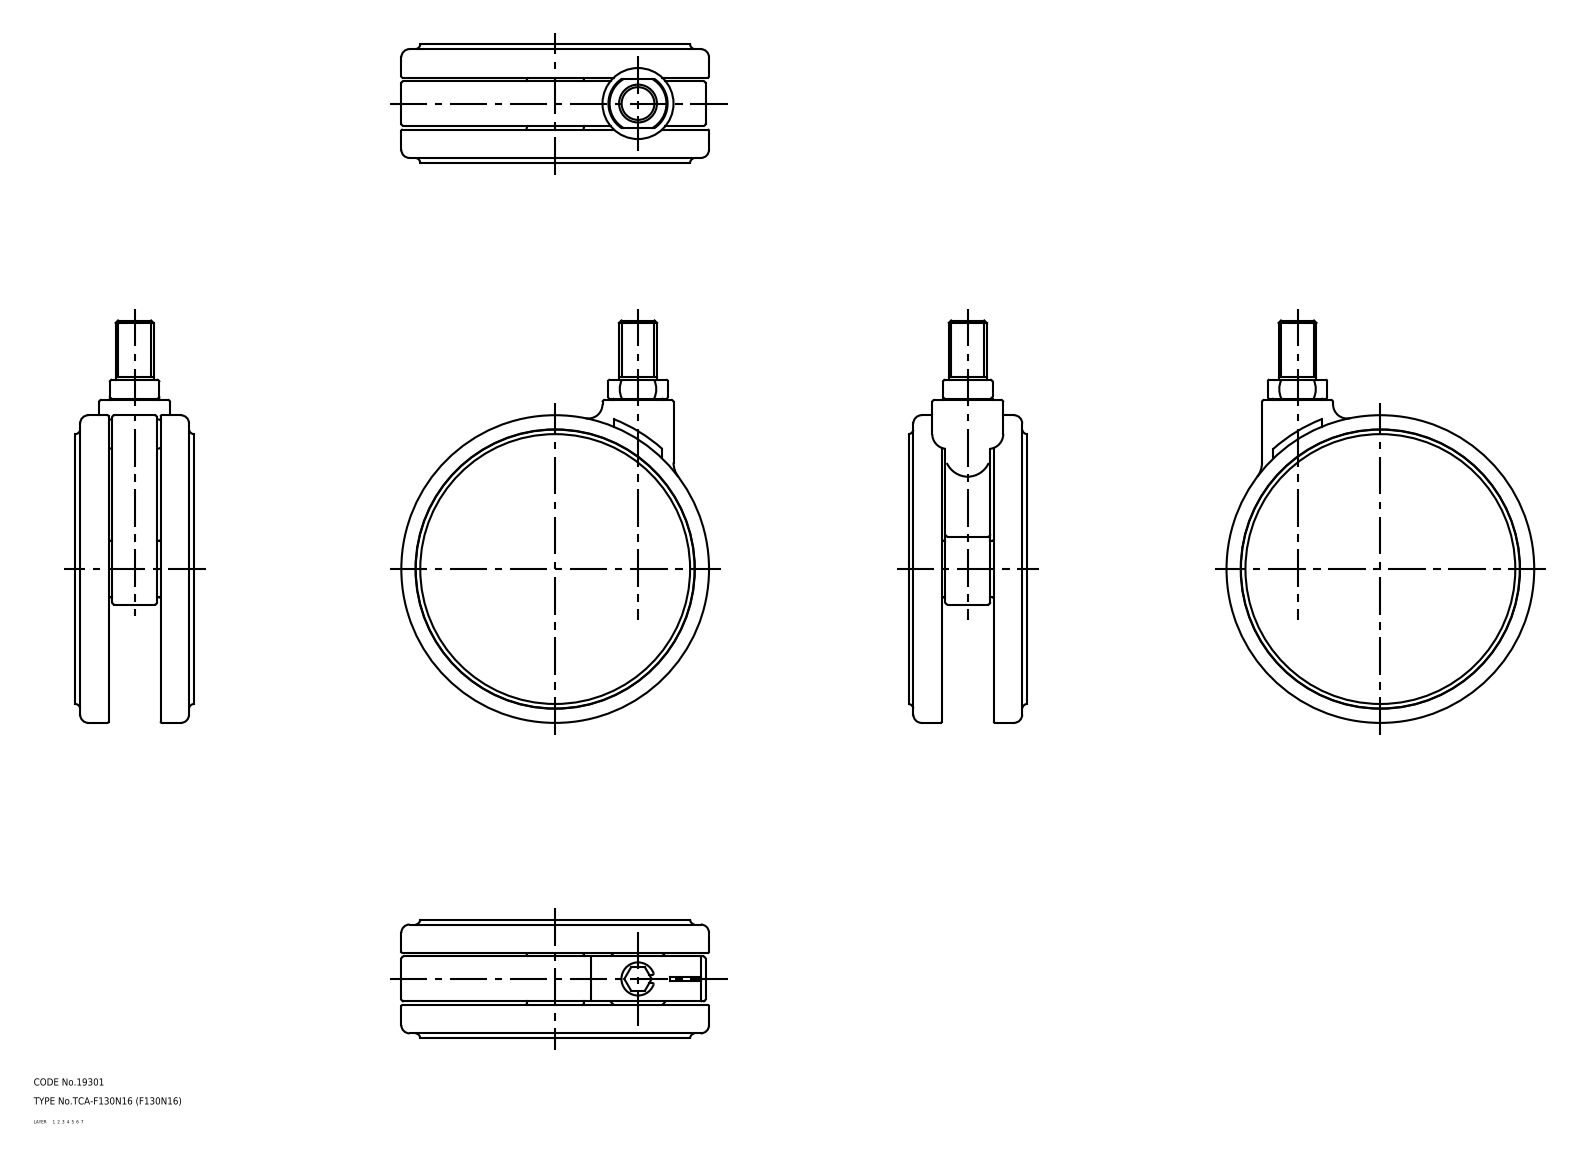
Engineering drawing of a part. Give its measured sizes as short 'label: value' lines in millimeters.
name: 67119534; 67119547; 67119560; 67119573
written by: CADfix (AUTOMOTIVE_DESIGN)
unit: mm
bodies: 4 solids, 148 faces (0 planar, 0 cylindrical, 148 other)
size: 170 × 130 × 50
volume: 455 379 mm³; area: 92 630 mm²
